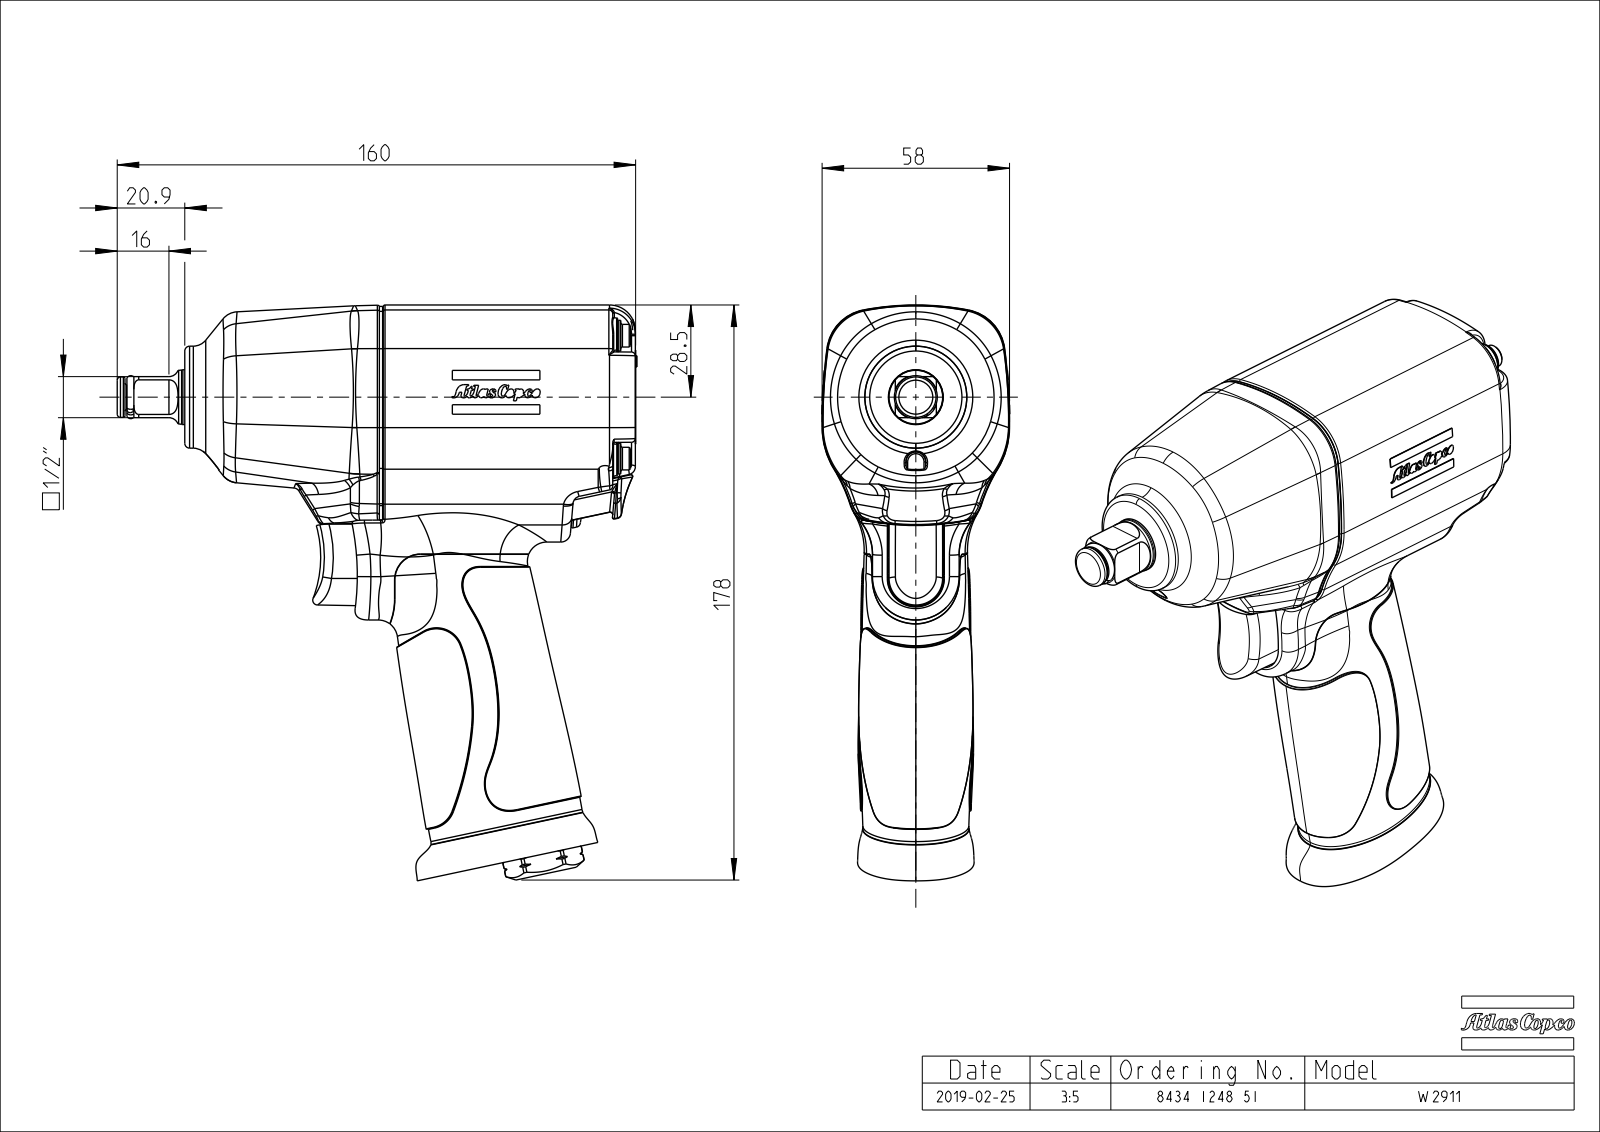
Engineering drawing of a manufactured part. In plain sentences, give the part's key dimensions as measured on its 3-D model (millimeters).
The part is named "8434124851_SW". Its 3-D file was written by "CREO PARAMETRIC BY PTC INC, 2018100 (CONFIG_CONTROL_DESIGN)". It is 2 solids with 4130 faces: 684 planar, 975 cylindrical and 2471 other. Overall it measures 178.06 by 160.8 by 58.16 millimeters. Its volume is 210 423 cubic millimeters and its surface area 124 723 square millimeters. Round holes: 8 of diameter 1.5, 1 of diameter 1, 1 of diameter 2, 1 of diameter 2.1, 1 of diameter 3, 1 of diameter 3.1, 1 of diameter 4.2, 1 of diameter 6.3, 1 of diameter 10.9, 1 of diameter 24, 1 of diameter 25, 1 of diameter 49. Round bosses or shafts: 5 of diameter 9.5, 4 of diameter 7, 4 of diameter 3.9, 1 of diameter 37, 1 of diameter 34.8, 1 of diameter 32.3, 1 of diameter 22, 1 of diameter 16.95. Partial cylindrical surfaces (rounded edges, fillets, slot ends): 120 of radius 0.3, 110 of radius 0.2, 78 of radius 0.5, 29 of radius 1, 25 of radius 0.1, 22 of radius 0.8, 19 of radius 1.2, 13 of radius 0.6. The main face-to-face distances are 9.8, 9.74, 109.25, 109.19, 112.62, 112.56, 3.37, 139.34, 77.2, 77.14. The hole center spacings are 4.35, 9, 4.81, 4.97, 9.77, 9.99, 10, 11.35.
